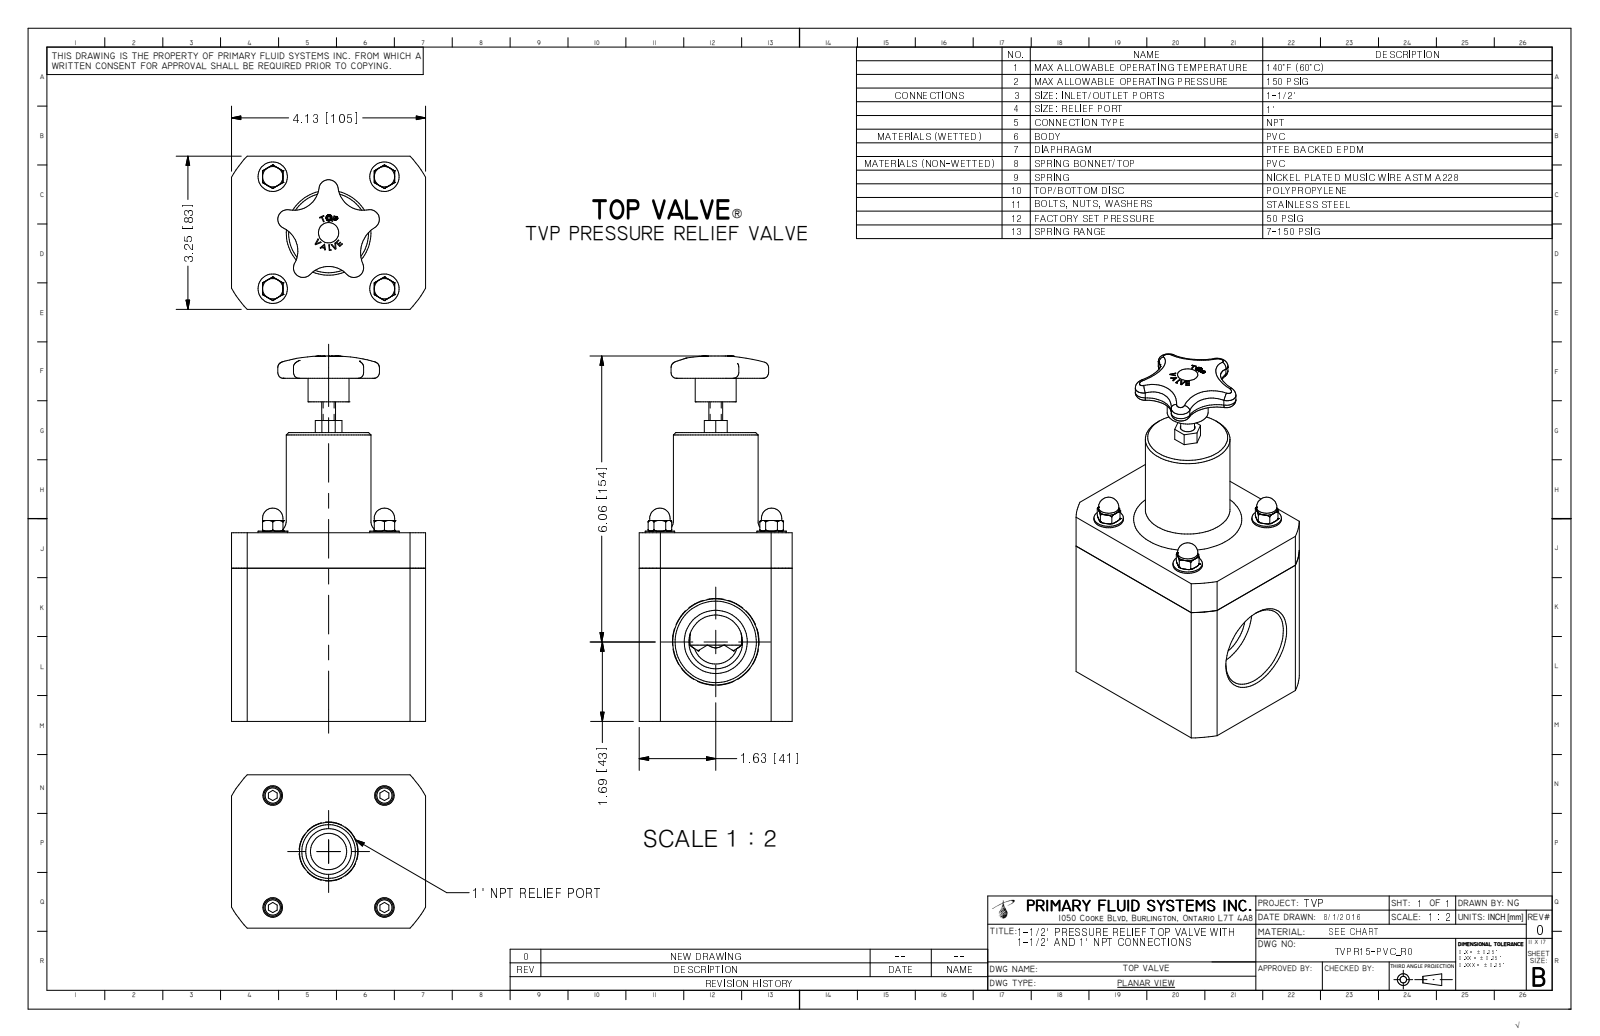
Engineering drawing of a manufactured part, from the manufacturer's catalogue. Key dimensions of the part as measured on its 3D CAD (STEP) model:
Part name (STEP PRODUCT): TVPR15-PVC_R0
STEP written by: Autodesk Inventor 2009 (AUTOMOTIVE_DESIGN)
Units: inches
Bodies: 1 solid, 351 faces (148 planar, 49 cylindrical, 154 other)
Overall size (bounding box): 7.75 × 4.125 × 3.25
Volume: 53.95 in³ · Surface area: 128.6 in²
Round holes (diameter × count): ⌀0.175 ×4, ⌀0.281 ×1, ⌀1.14 ×1, ⌀1.727 ×1
Round bosses / shafts (diameter × count): ⌀0.625 ×4, ⌀0.433 ×4, ⌀0.375 ×4, ⌀1.8 ×1, ⌀0.87 ×1, ⌀0.293 ×1, ⌀0.25 ×1
Partial cylindrical surfaces — rounded edges, fillets, slot ends (radius × count): R0.085 ×5, R0.205 ×5, R0.536 ×4, R0.656 ×4, R0.625 ×1, R0.745 ×1, R2.375 ×1
Main face-to-face distances: 3.25, 4, 4.125, 1, 3.125, 2.125, 6.125, 0.8, 3.2, 5.325
Hole centre spacings: 1.679, 1.68, 2.375, 2.375, 3.359
